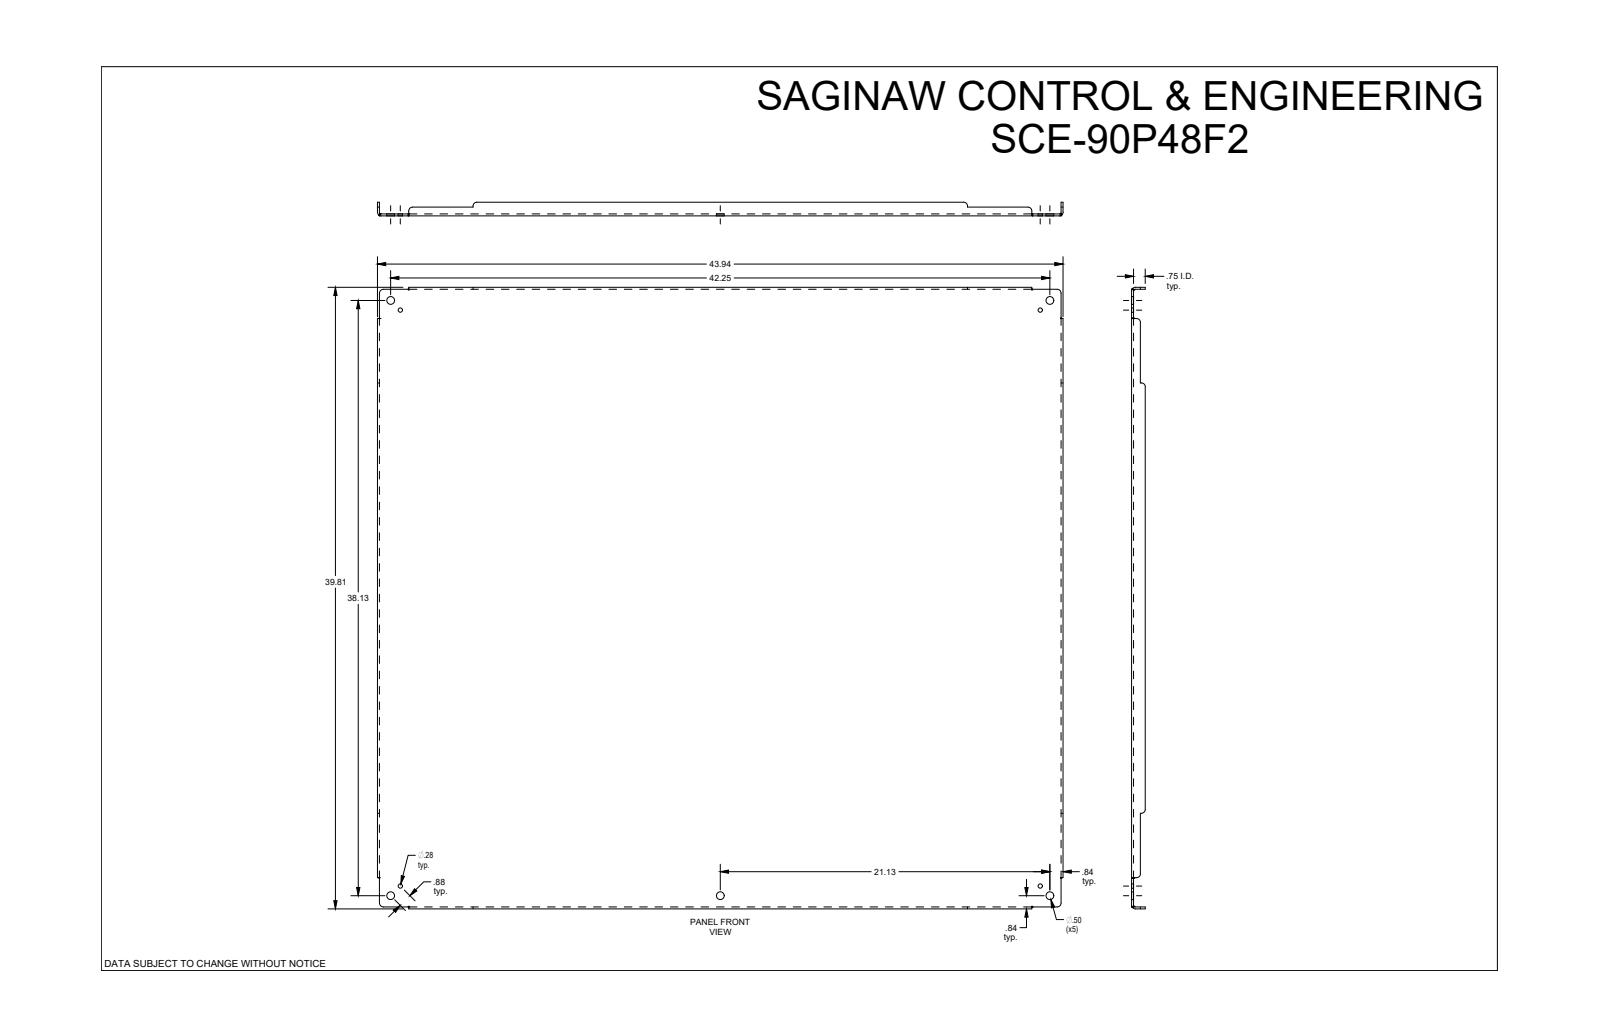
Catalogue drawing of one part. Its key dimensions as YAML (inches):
part_name: "SCE-90P48F2"
step_written_by: "SolidWorks 2019 (AUTOMOTIVE_DESIGN)"
units: inches
bodies: {solids: 1, faces: 107, planar: 46, cylindrical: 37, other: 24}
overall_size: [43.938, 39.813, 0.875]
volume: 229.7
surface_area: 3698
round_holes:
  - {diameter: 0.5, count: 5}
  - {diameter: 0.281, count: 4}
partial_cylinders:
  - {radius: 0.25, count: 12}
  - {radius: 0.112, count: 4}
  - {radius: 0.237, count: 4}
face_to_face_distances: [0.125, 0.125, 39.687, 43.813, 39.562, 39.813, 43.687, 43.938, 0.75, 0.875]
hole_center_spacings: [0.875, 37.511, 41.636, 56.035, 20.516, 21.125, 36.887, 38.125]
